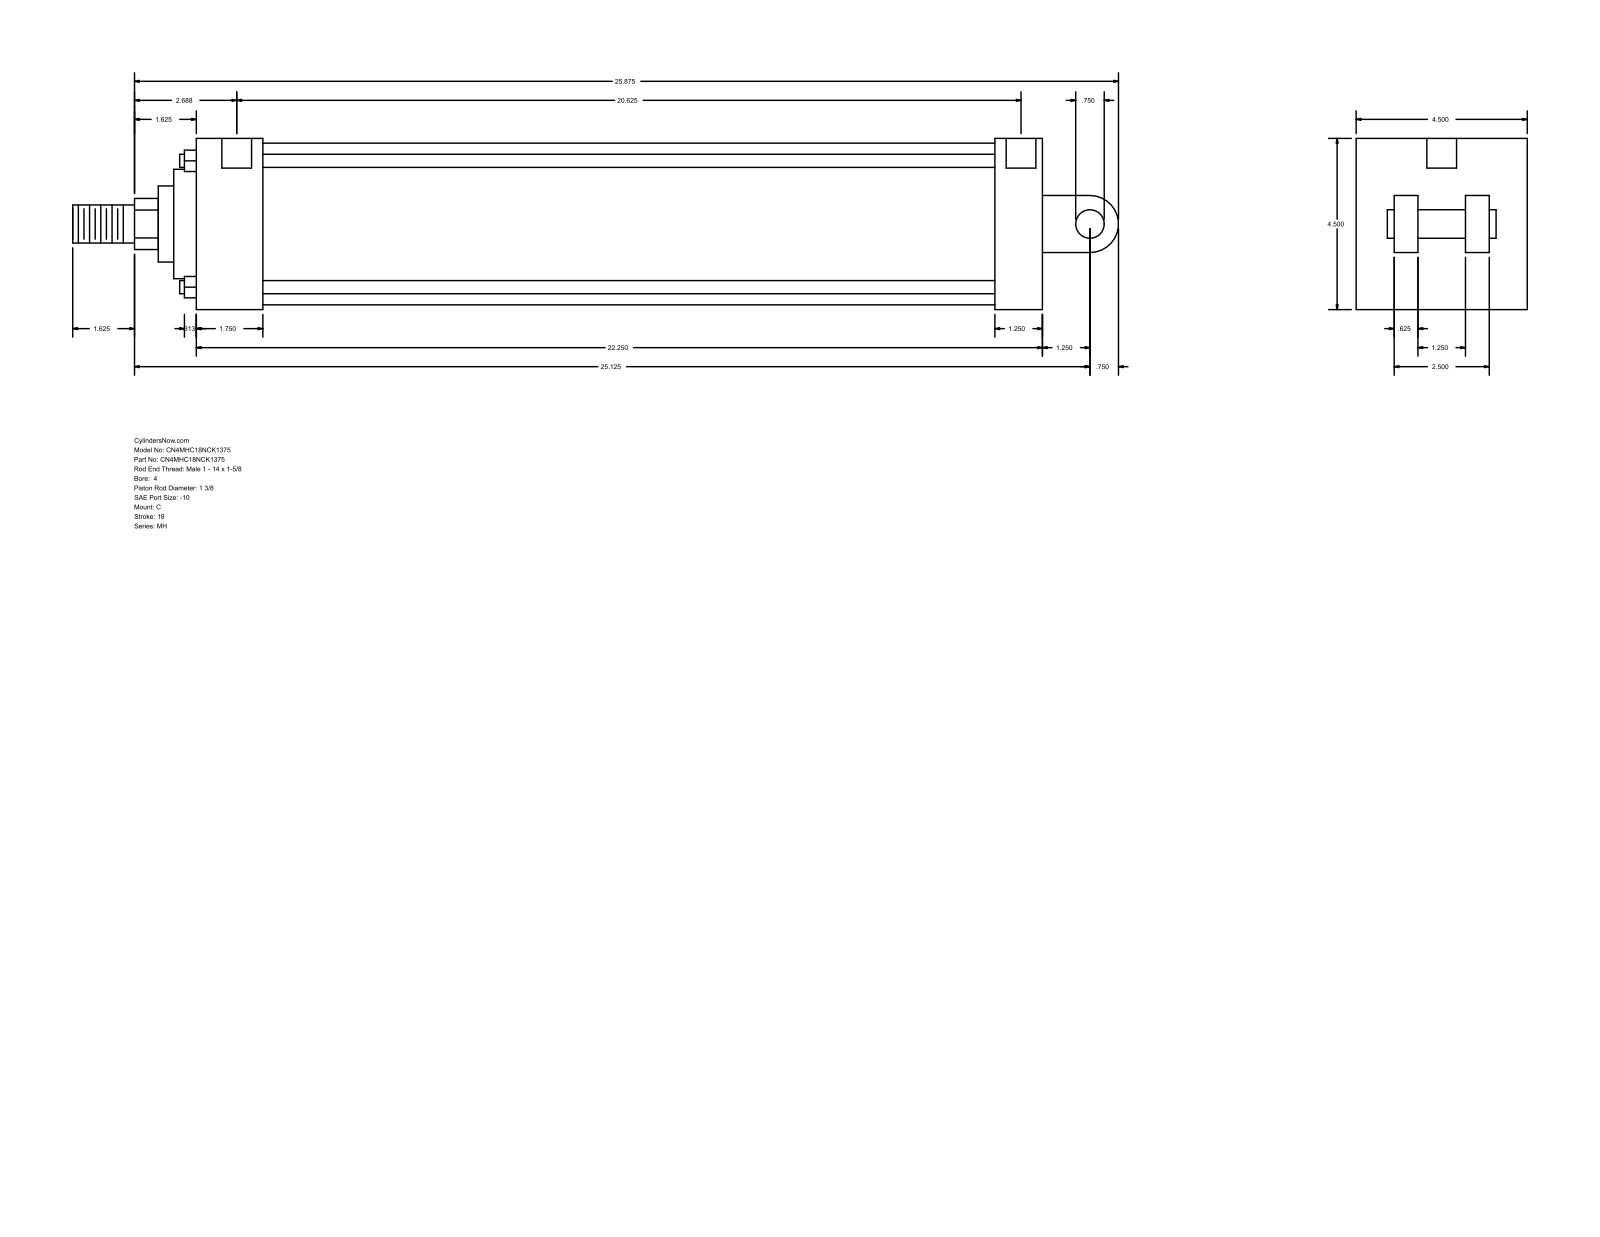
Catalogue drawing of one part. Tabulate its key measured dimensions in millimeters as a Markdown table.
| quantity | value |
| --- | --- |
| part name | MH_C__0400_1.375 |
| STEP written by | GSSL Pune (CONFIG_CONTROL_DESIGN) |
| units | millimeters |
| bodies | 0 solids, 101 faces (71 planar, 30 cylindrical, 0 other) |
| overall size | 698.5 × 114.3 × 114.3 |
| round holes (diameter × count) | 8.73 × 4, 19.84 × 2 |
| round bosses / shafts (diameter × count) | 8.76 × 4, 107.95 × 1, 73.03 × 1, 50.8 × 1, 34.92 × 1, 25.4 × 1, 19.05 × 1 |
| partial cylindrical surfaces (radius × count) | 17.06 × 1, 19.05 × 1 |
| main face-to-face distances | 114.3, 565.15, 44.45, 533.4, 488.95, 520.7, 31.75, 41.27, 73.03, 38.1 |
| hole center spacings | 1.59, 525.47, 527.06, 523.88 |
